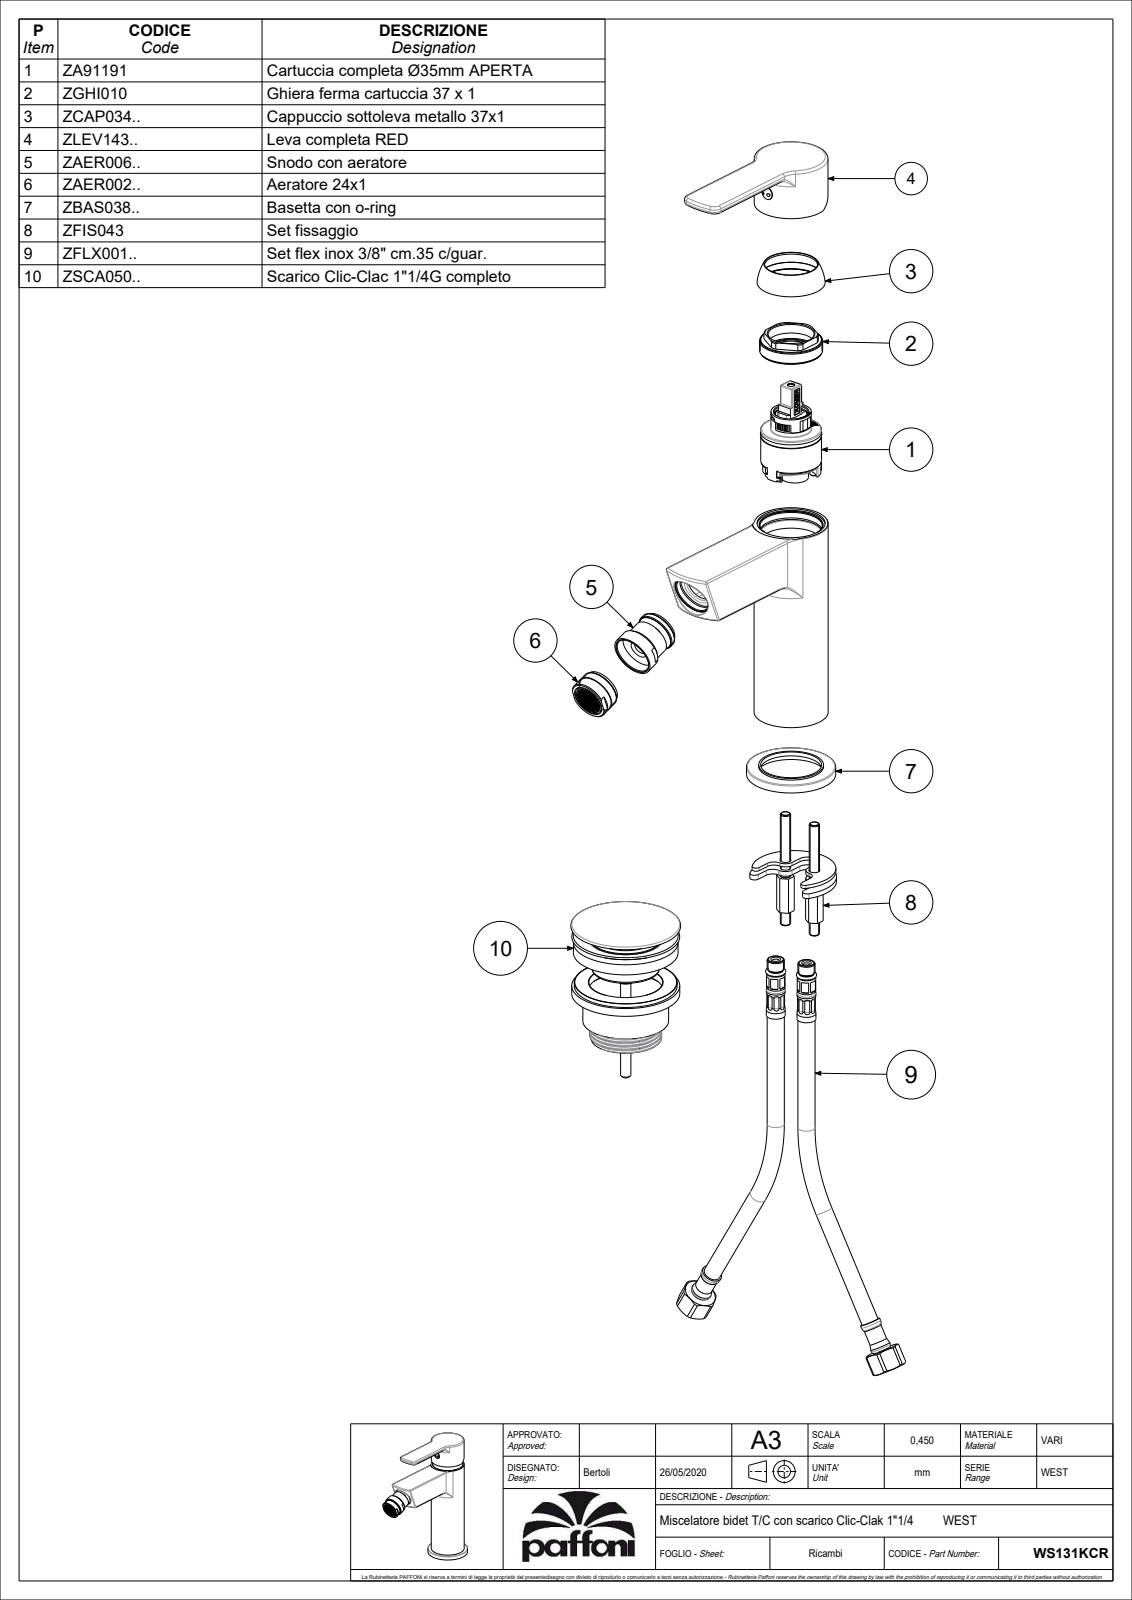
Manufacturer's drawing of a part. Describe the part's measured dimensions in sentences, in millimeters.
The part is named "WS131CR". Its 3-D file was written by "CREO PARAMETRIC BY PTC INC, 2020044 (CONFIG_CONTROL_DESIGN)". It is 3 solids with 3482 faces: 2447 planar, 567 cylindrical and 468 other. Overall it measures 162.55 by 148.2 by 52 millimeters. Its volume is 176 488 cubic millimeters and its surface area 106 694 square millimeters. Round holes: 3 of diameter 4.6, 3 of diameter 8, 2 of diameter 5.5, 2 of diameter 7, 2 of diameter 9, 2 of diameter 11, 1 of diameter 3, 1 of diameter 3.4, 1 of diameter 3.5, 1 of diameter 4, 1 of diameter 4.5, 1 of diameter 15.5. Round bosses or shafts: 2 of diameter 10.8, 2 of diameter 8.2, 2 of diameter 6, 2 of diameter 4.8, 1 of diameter 52, 1 of diameter 43.2, 1 of diameter 43, 1 of diameter 42.6. Partial cylindrical surfaces (rounded edges, fillets, slot ends): 85 of radius 0.5, 33 of radius 1.5, 19 of radius 1, 9 of radius 2, 6 of radius 1.7, 4 of radius 0.8, 4 of radius 5, 4 of radius 5.8. The main face-to-face distances are 3.5, 27.5, 4.5, 35.55, 25.5, 31.05, 31, 29, 60.05, 64.55. The hole center spacings are 0.5, 8.6, 9.01, 13.45, 14.5, 15.07, 15.13, 21.93.
